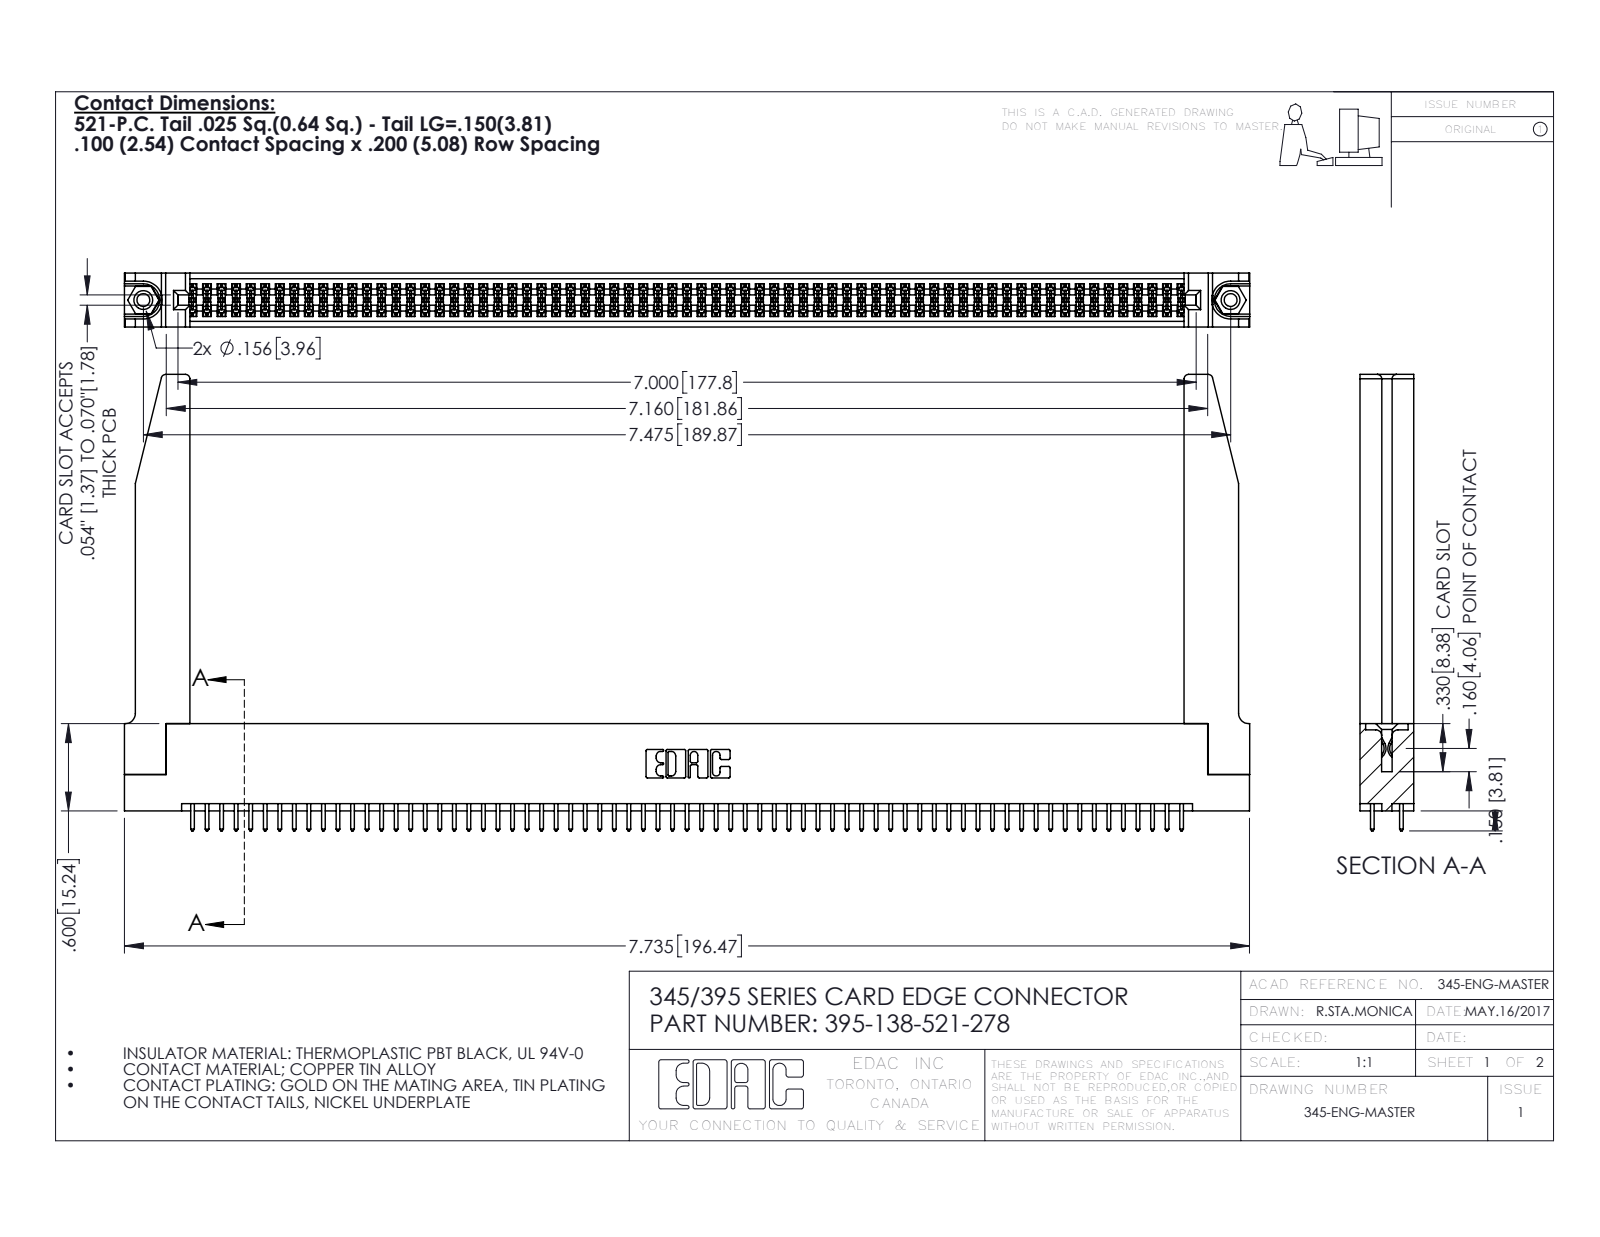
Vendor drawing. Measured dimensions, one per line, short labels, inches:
name: 345-250-001_345-250-001-102; 345 Part_Flush Mounting Lugs - 0.156 Dia-TH; 345-292-001_345-293-121; 345-220-078_345-220-078 (+1 more)
written by: SolidWorks 2016 (CONFIG_CONTROL_DESIGN)
unit: in
bodies: 143 solids, 7260 faces (4776 planar, 2432 cylindrical, 52 other)
size: 7.736 × 3.137 × 0.37
volume: 1.651 in³; area: 55.02 in²
holes: 2× ⌀0.089, 2× ⌀0.125, 2× ⌀0.156, 1× ⌀0.064
bosses: 2× ⌀0.155
rounds: 207× R0.006, 138× R0.01, 22× R0.01, 8× R0.03, 6× R0.007, 6× R0.031, 3× R0.026, 2× R0.014
face distances: 0.072, 0.298, 0.37, 0.2, 0.098, 0.272, 0.025, 0.225, 0.175, 0.149
hole spacings: 0.27, 7.239, 7.475
